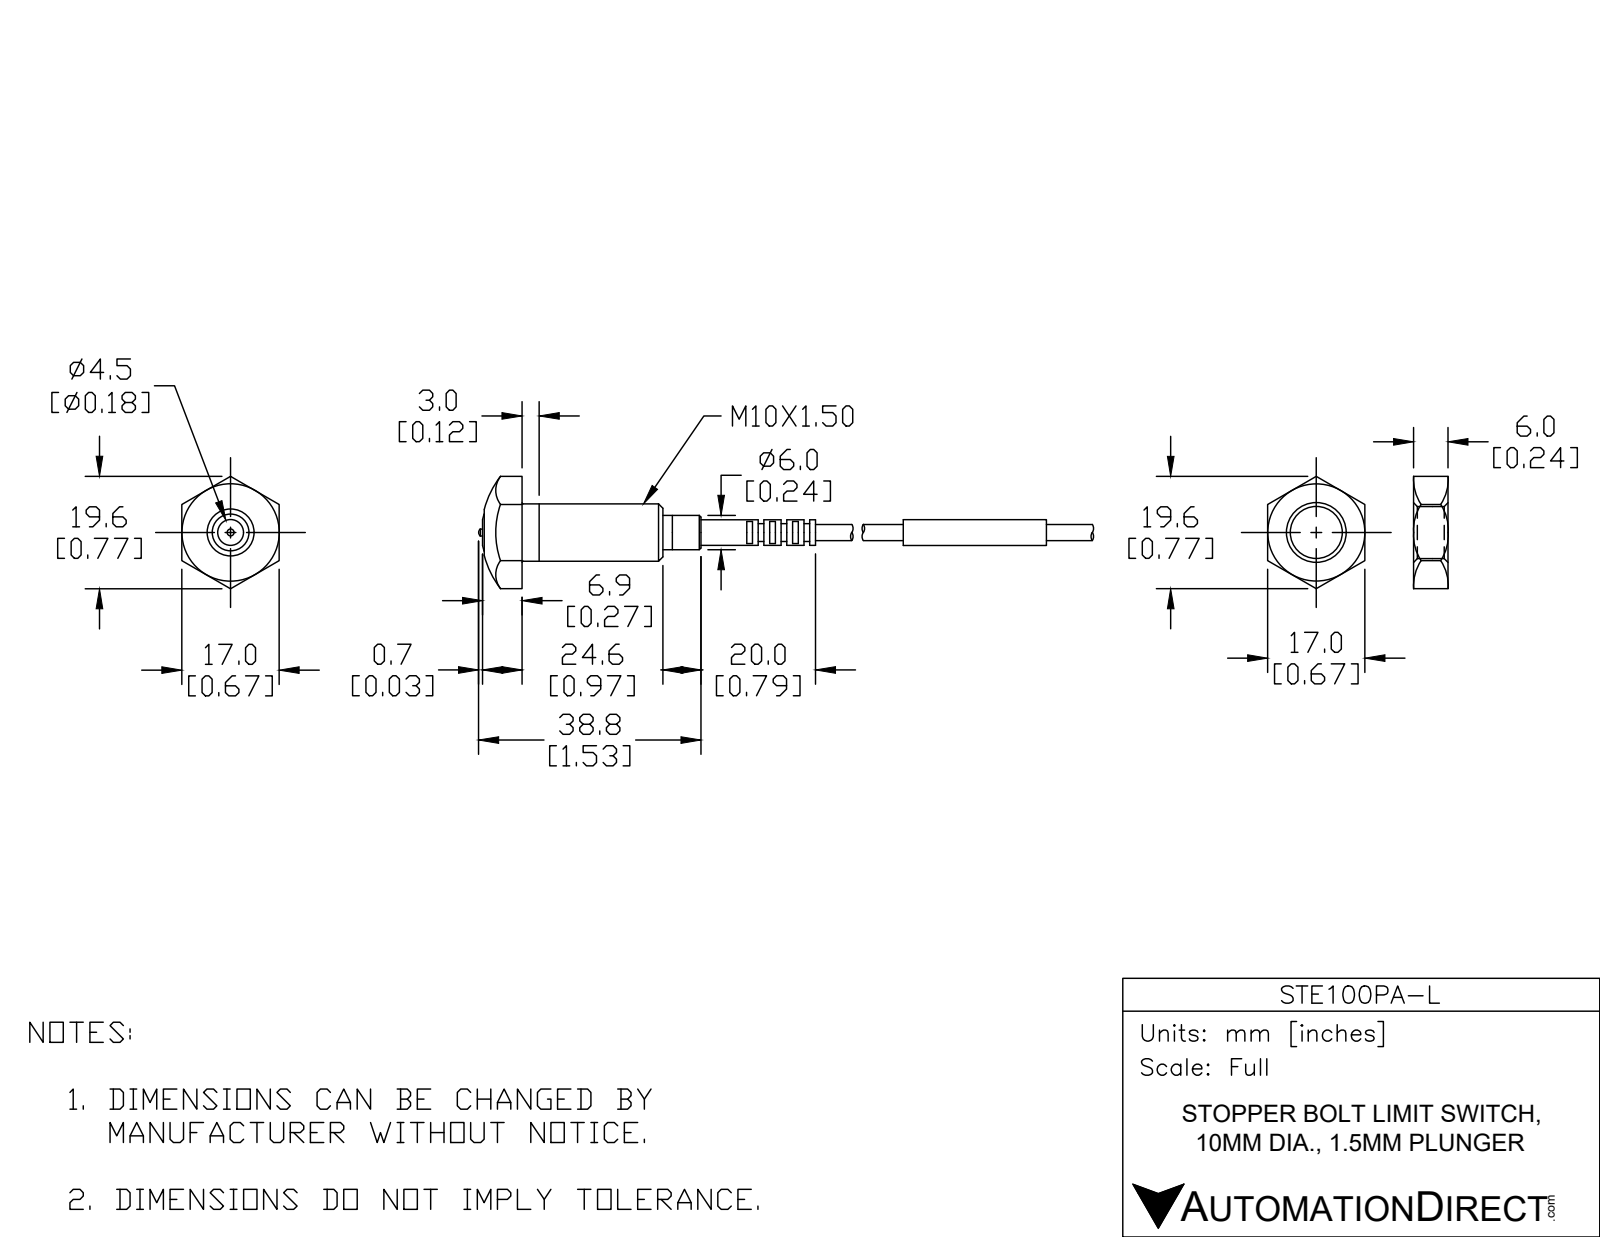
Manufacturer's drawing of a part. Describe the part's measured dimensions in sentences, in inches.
The part is named "STE100PA-L". Its 3-D file was written by "SolidWorks 2017 (CONFIG_CONTROL_DESIGN)". It is 2 solids with 167 faces: 65 planar, 75 cylindrical and 27 other. Overall it measures 4.324 by 0.772 by 0.669 inches. Its volume is 0.249 cubic inches and its surface area 4.559 square inches. Round bosses or shafts: 1 of diameter 0.394, 1 of diameter 0.252, 1 of diameter 0.236, 1 of diameter 0.177, 1 of diameter 0.175, 1 of diameter 0.122, 1 of diameter 0.11, 1 of diameter 0.047. Partial cylindrical surfaces (rounded edges, fillets, slot ends): 1 of radius 0.386. The main face-to-face distances are 0.669, 0.039, 0.079, 0.118, 0.157, 0.197, 0.236, 0.315, 0.276, 0.969.
